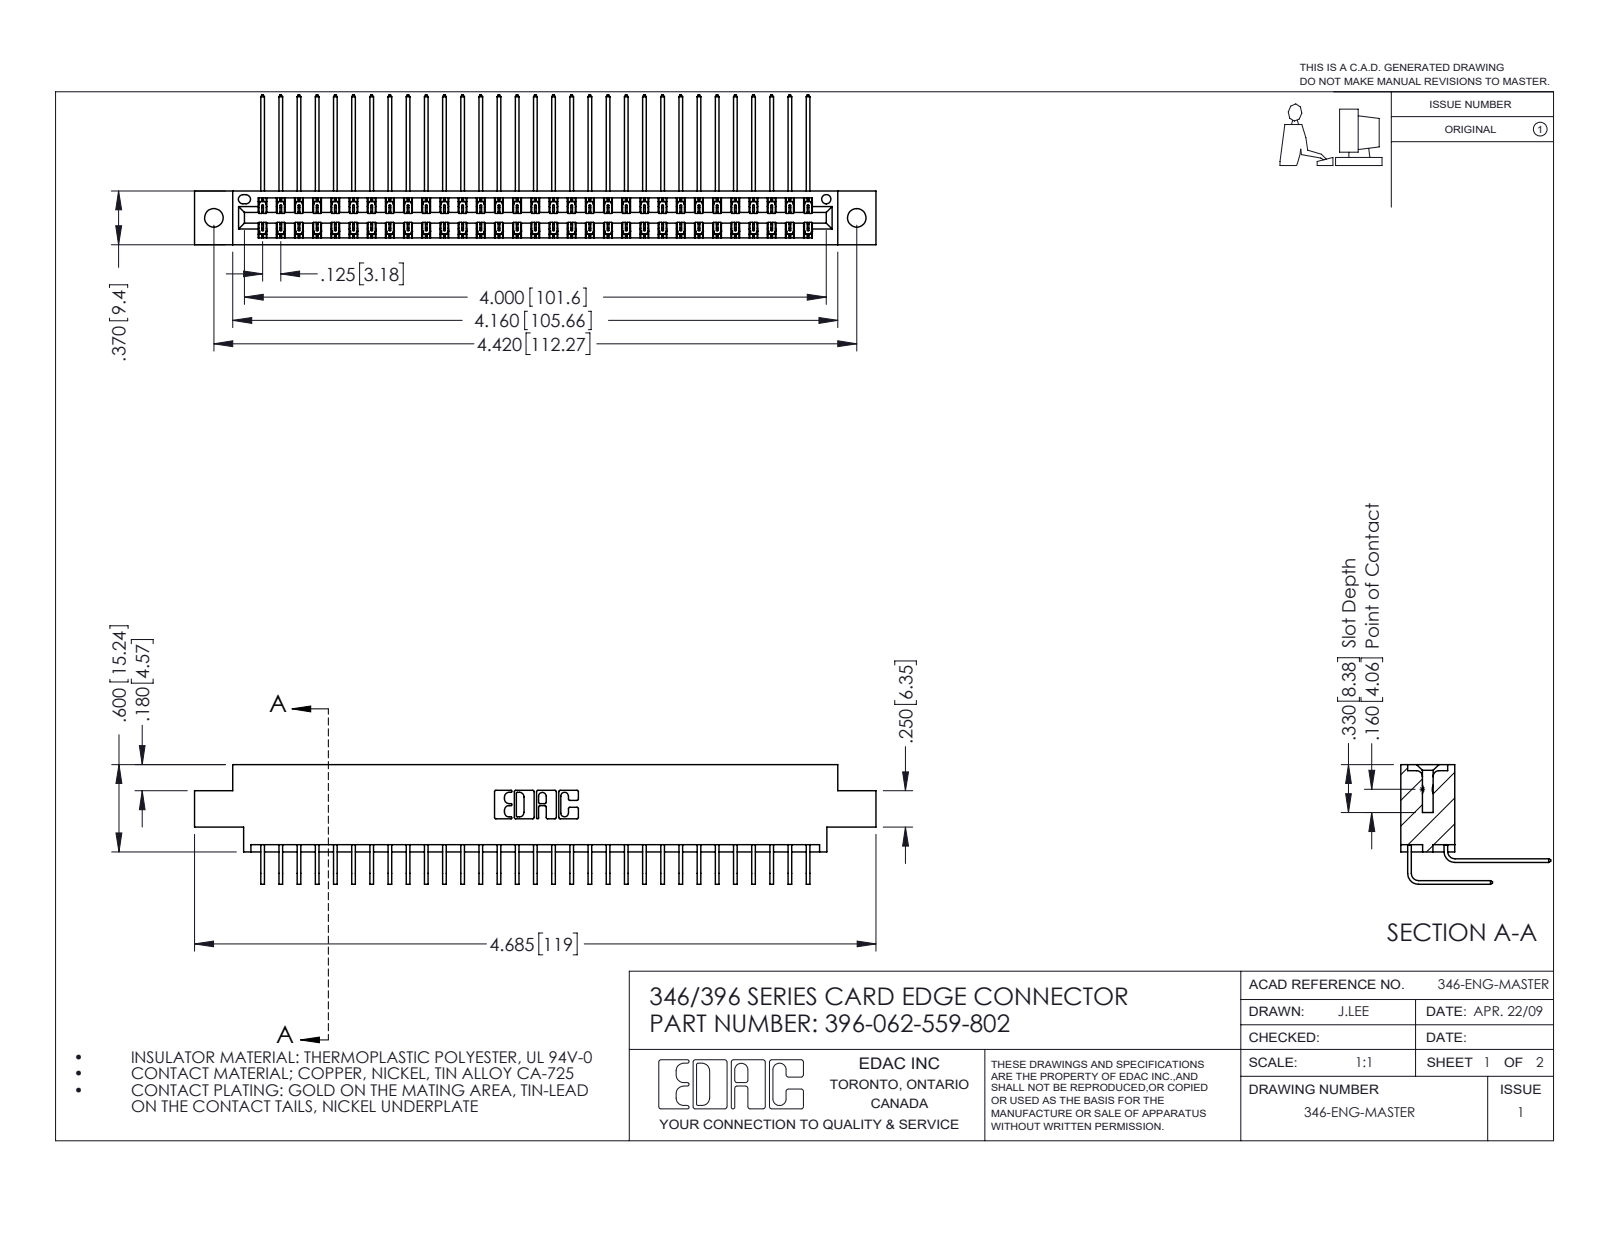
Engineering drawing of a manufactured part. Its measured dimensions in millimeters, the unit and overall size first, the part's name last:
Units: millimetres
Overall size (bounding box): 119 × 26.2 × 20.9
Round holes (diameter × count): ⌀3.3 ×2, ⌀1.6 ×1
Partial cylindrical surfaces — rounded edges, fillets, slot ends (radius × count): R0.2 ×93, R0.3 ×22, R0.2 ×6, R0.8 ×6, R0.7 ×3, R0.4 ×2, R0.6 ×2, R0.6 ×2
Main face-to-face distances: 1.2, 8.2, 0.6, 9.4, 6.4, 1.8, 7.6, 7, 3.8, 5.6
Hole centre spacings: 6.2, 107, 112.3
Volume: 11 700 mm³ · Surface area: 17 520 mm²
Bodies: 63 solids, 3474 faces (2374 planar, 1100 cylindrical, 0 other)
Part name (STEP PRODUCT): 345-292-001_559 Tail - 2; 345-292-001_558 559 Tail - 1; 346 Part_0.170 Offset - 0.128 Dia; 396-062-559-802
STEP written by: SolidWorks 2016 (CONFIG_CONTROL_DESIGN)
